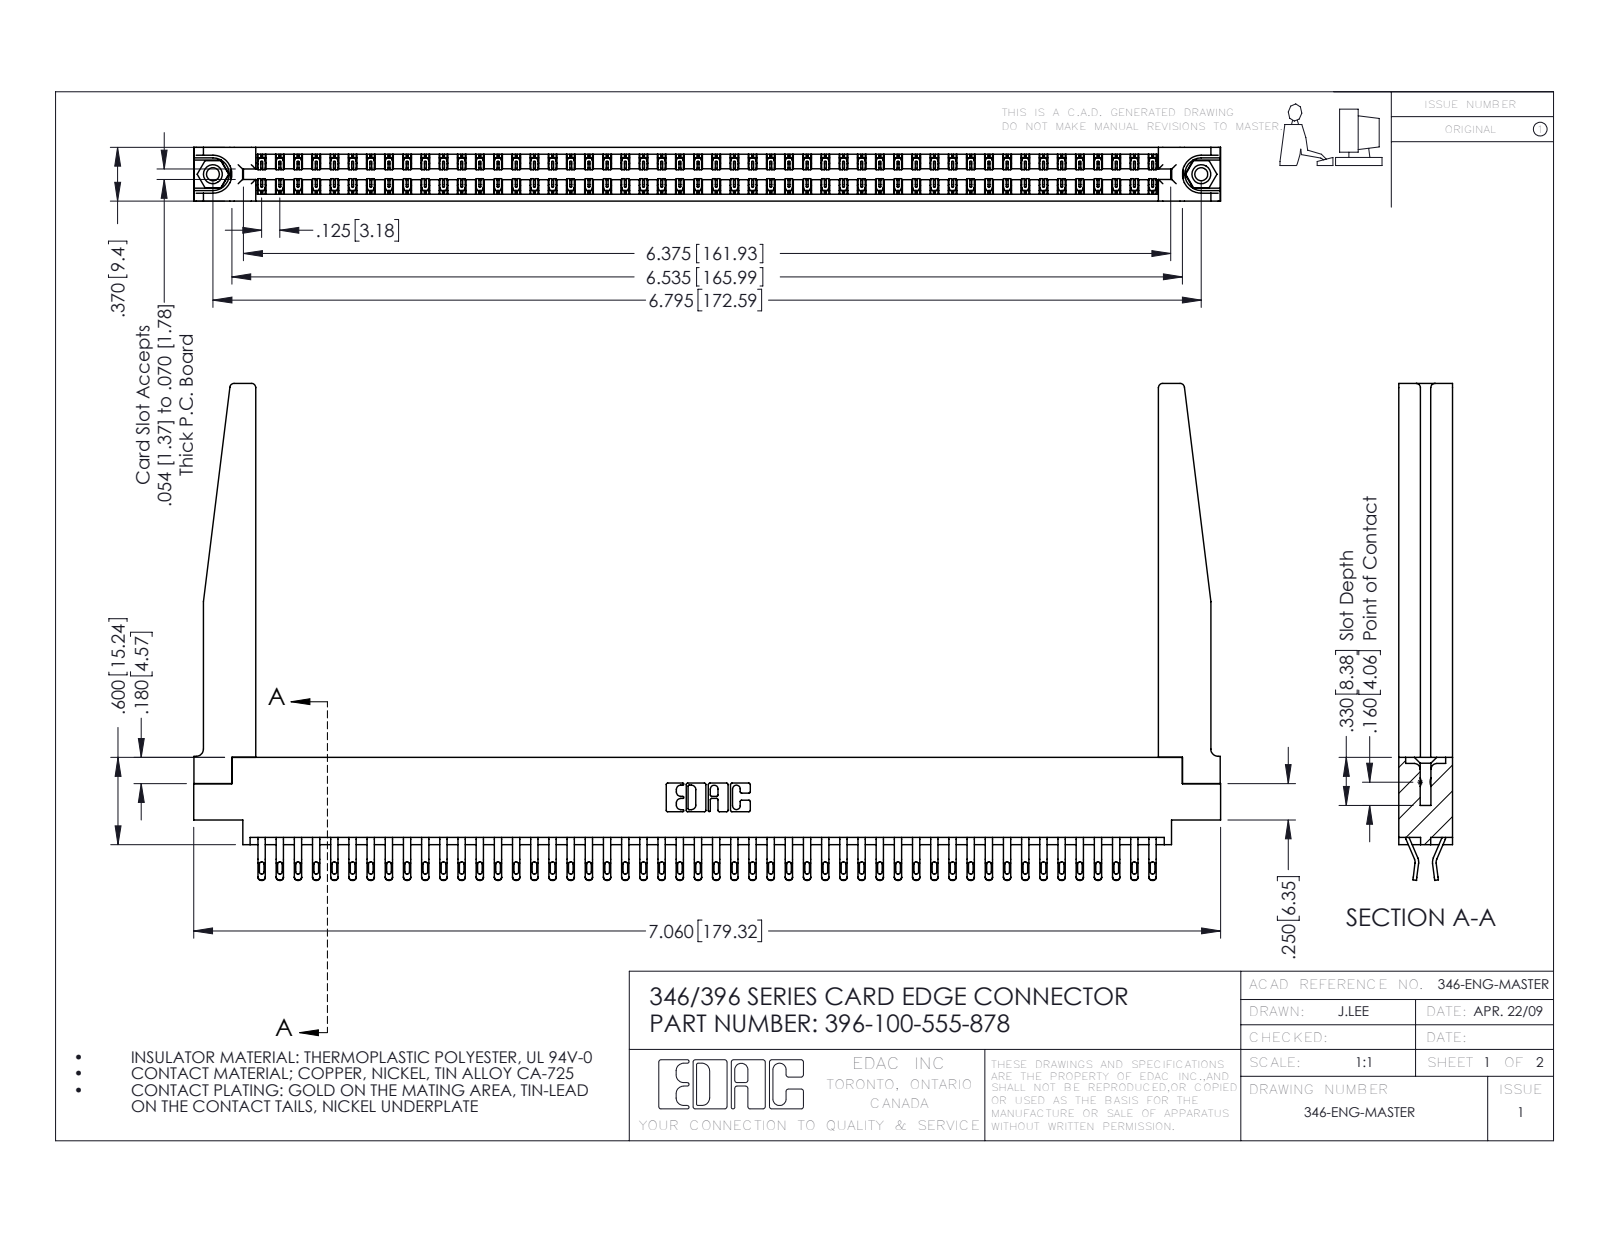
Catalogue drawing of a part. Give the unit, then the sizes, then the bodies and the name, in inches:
Units: inches
Overall size (bounding box): 7.06 × 3.415 × 0.37
Round holes (diameter × count): ⌀0.089 ×2, ⌀0.125 ×2, ⌀0.156 ×2, ⌀0.064 ×1
Round bosses / shafts (diameter × count): ⌀0.155 ×2
Partial cylindrical surfaces — rounded edges, fillets, slot ends (radius × count): R0.016 ×200, R0.02 ×200, R0.006 ×150, R0.01 ×22, R0.03 ×8, R0.007 ×6, R0.031 ×6, R0.05 ×4
Main face-to-face distances: 0.37, 0.048, 0.322, 0.072, 0.148, 0.15, 0.25, 0.025, 0.298, 0.275
Hole centre spacings: 0.246, 6.586, 6.795
Volume: 1.501 in³ · Surface area: 49.89 in²
Bodies: 105 solids, 6160 faces (3522 planar, 2586 cylindrical, 52 other)
Part name (STEP PRODUCT): 346 Part_0.170 Offset - 0.156 Dia-TH; 345-292-001_555 Tail; 346-220-078_345-220-078; 345-250-001_345-250-001-102 (+1 more)
STEP written by: SolidWorks 2016 (CONFIG_CONTROL_DESIGN)
